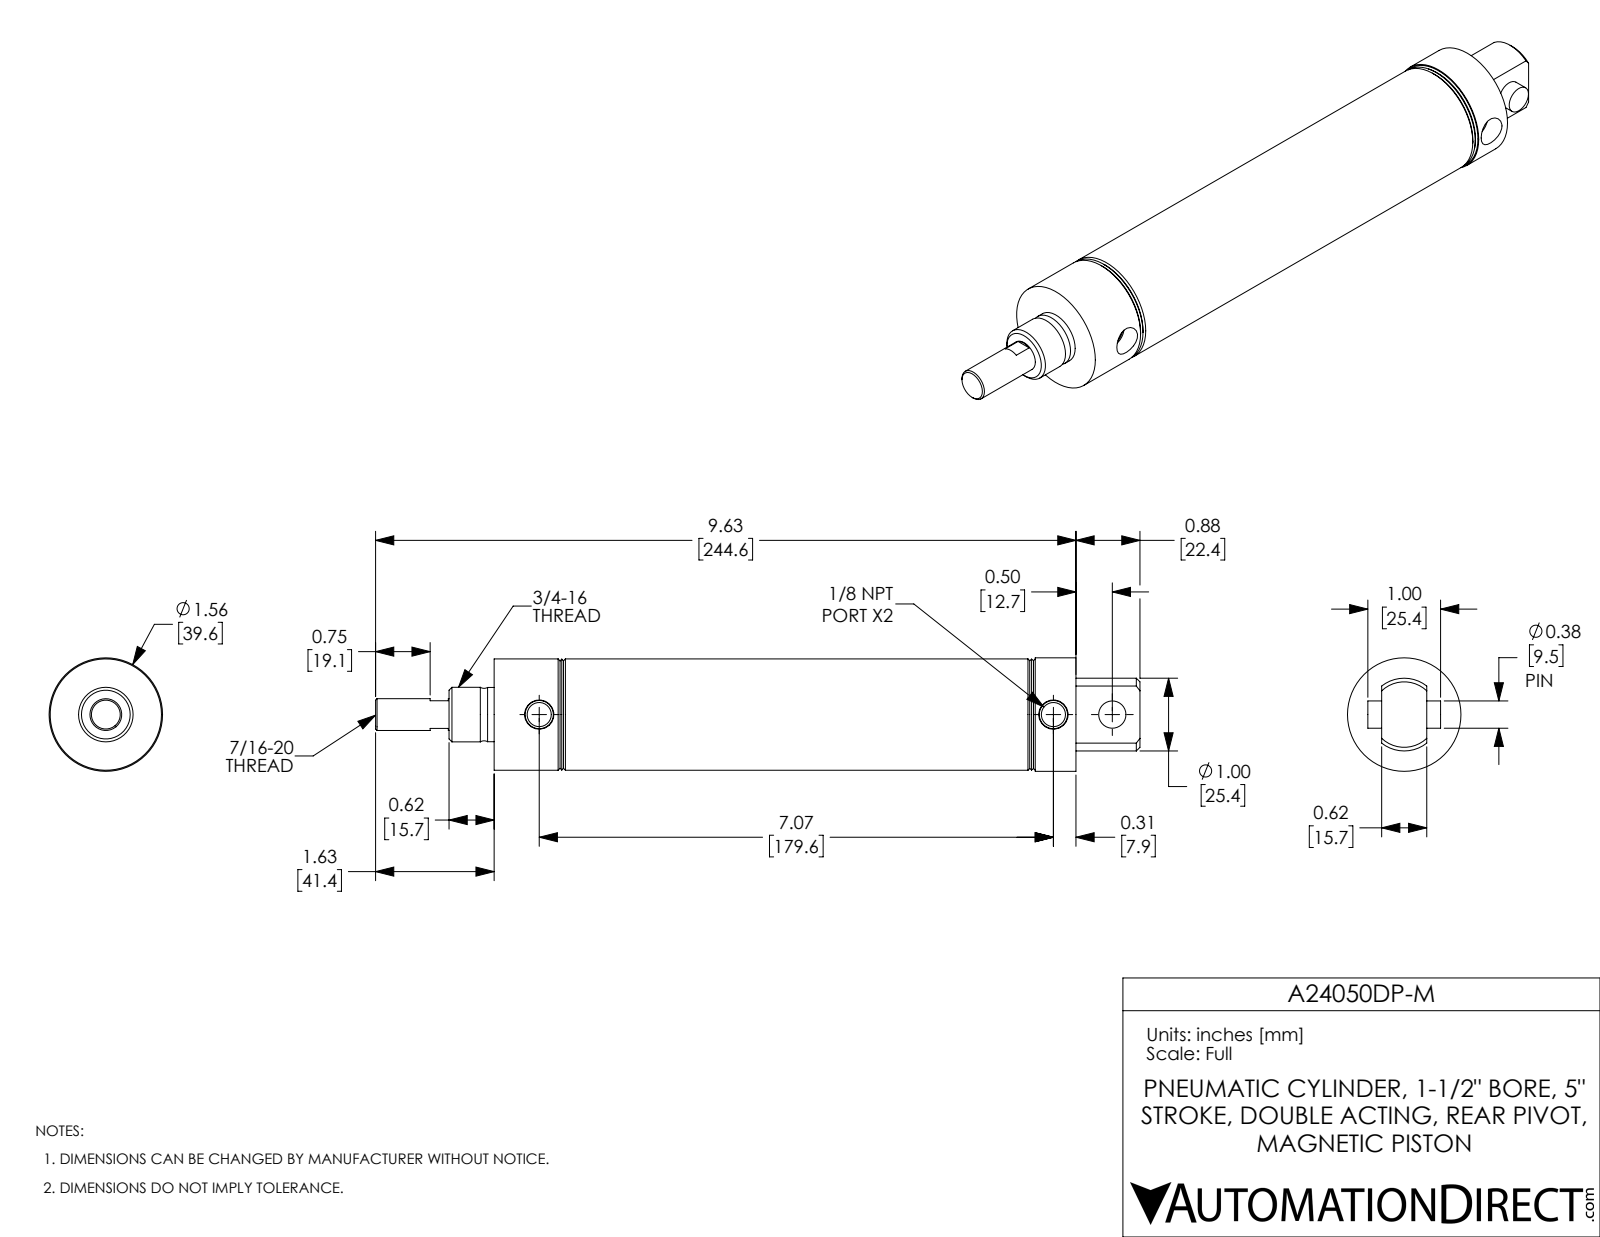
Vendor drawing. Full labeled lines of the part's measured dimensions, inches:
Part name (STEP PRODUCT): A24050DP-M; A24050DP-M-MainBody; A24050DP-M-Pin; A24050DP-M-Rod
STEP written by: SolidWorks 2017 (AUTOMOTIVE_DESIGN)
Units: inches
Bodies: 3 solids, 84 faces (22 planar, 28 cylindrical, 34 other)
Overall size (bounding box): 10.51 × 1.56 × 1.56
Volume: 7.516 in³ · Surface area: 97.95 in²
Round holes (diameter × count): ⌀0.332 ×2, ⌀0.375 ×1, ⌀0.437 ×1, ⌀1.5 ×1
Round bosses / shafts (diameter × count): ⌀1.56 ×1, ⌀1.53 ×1, ⌀0.75 ×1, ⌀0.746 ×1
Partial cylindrical surfaces — rounded edges, fillets, slot ends (radius × count): R0.5 ×1
Main face-to-face distances: 1.25, 6.75, 0.5, 5.5, 5, 6.25, 1.75, 8, 0.62, 0.88
Hole centre spacings: 0.81, 7.07, 7.88
